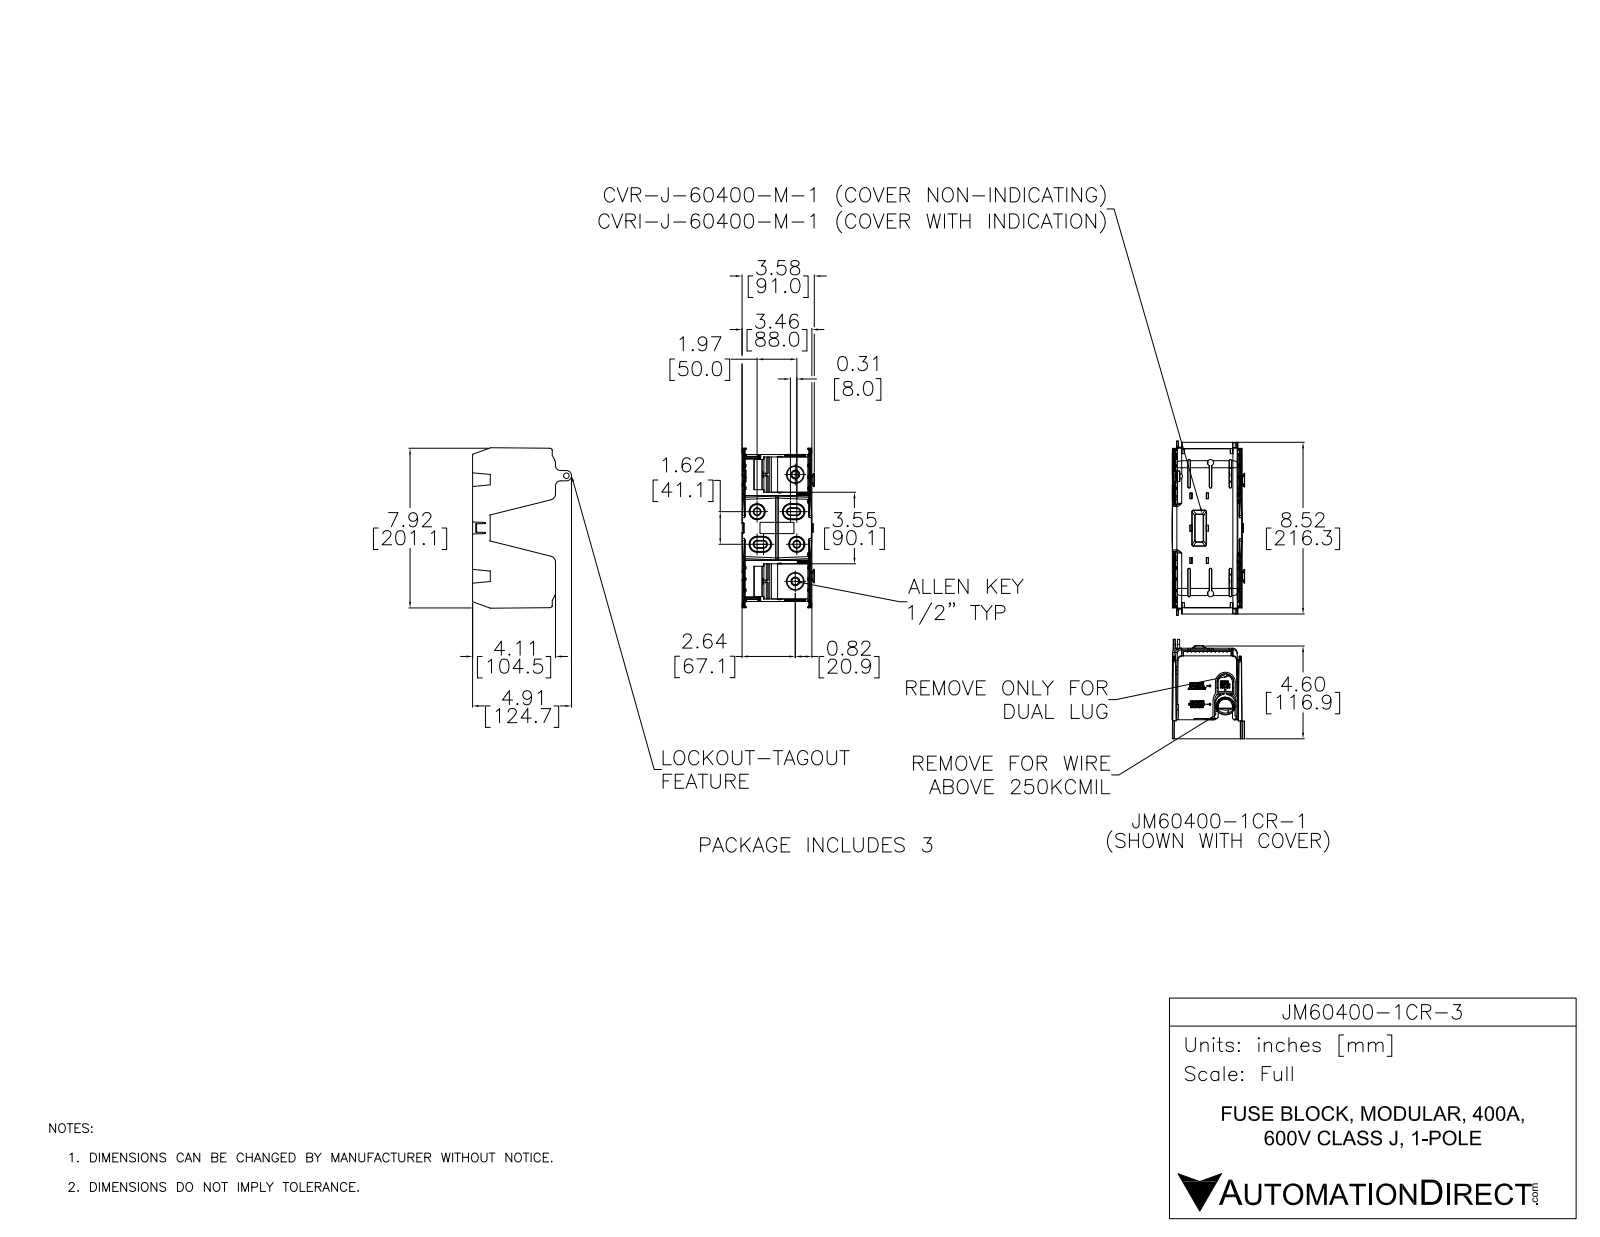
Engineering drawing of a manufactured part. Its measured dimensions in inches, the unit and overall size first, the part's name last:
Units: inches
Overall size (bounding box): 10.565 × 7.957 × 4.768
Round holes (diameter × count): ⌀0.937 ×3
Round bosses / shafts (diameter × count): ⌀0.196 ×12, ⌀0.875 ×6, ⌀0.28 ×6, ⌀0.277 ×1
Partial cylindrical surfaces — rounded edges, fillets, slot ends (radius × count): R0.02 ×382, R0.01 ×126, R0.015 ×56, R0.014 ×52, R0.01 ×48, R0.01 ×27, R0.119 ×26, R0.039 ×12
Main face-to-face distances: 3.482, 6.964, 3.336, 3.336, 0.95, 0.048, 3.478, 6.818, 0.146, 6.818
Hole centre spacings: 3.482, 6.964
Bodies: 0 solids, 2916 faces (861 planar, 1254 cylindrical, 801 other)
Part name (STEP PRODUCT): JM60400-1CR-3
STEP written by: SolidWorks 2021 (CONFIG_CONTROL_DESIGN)
